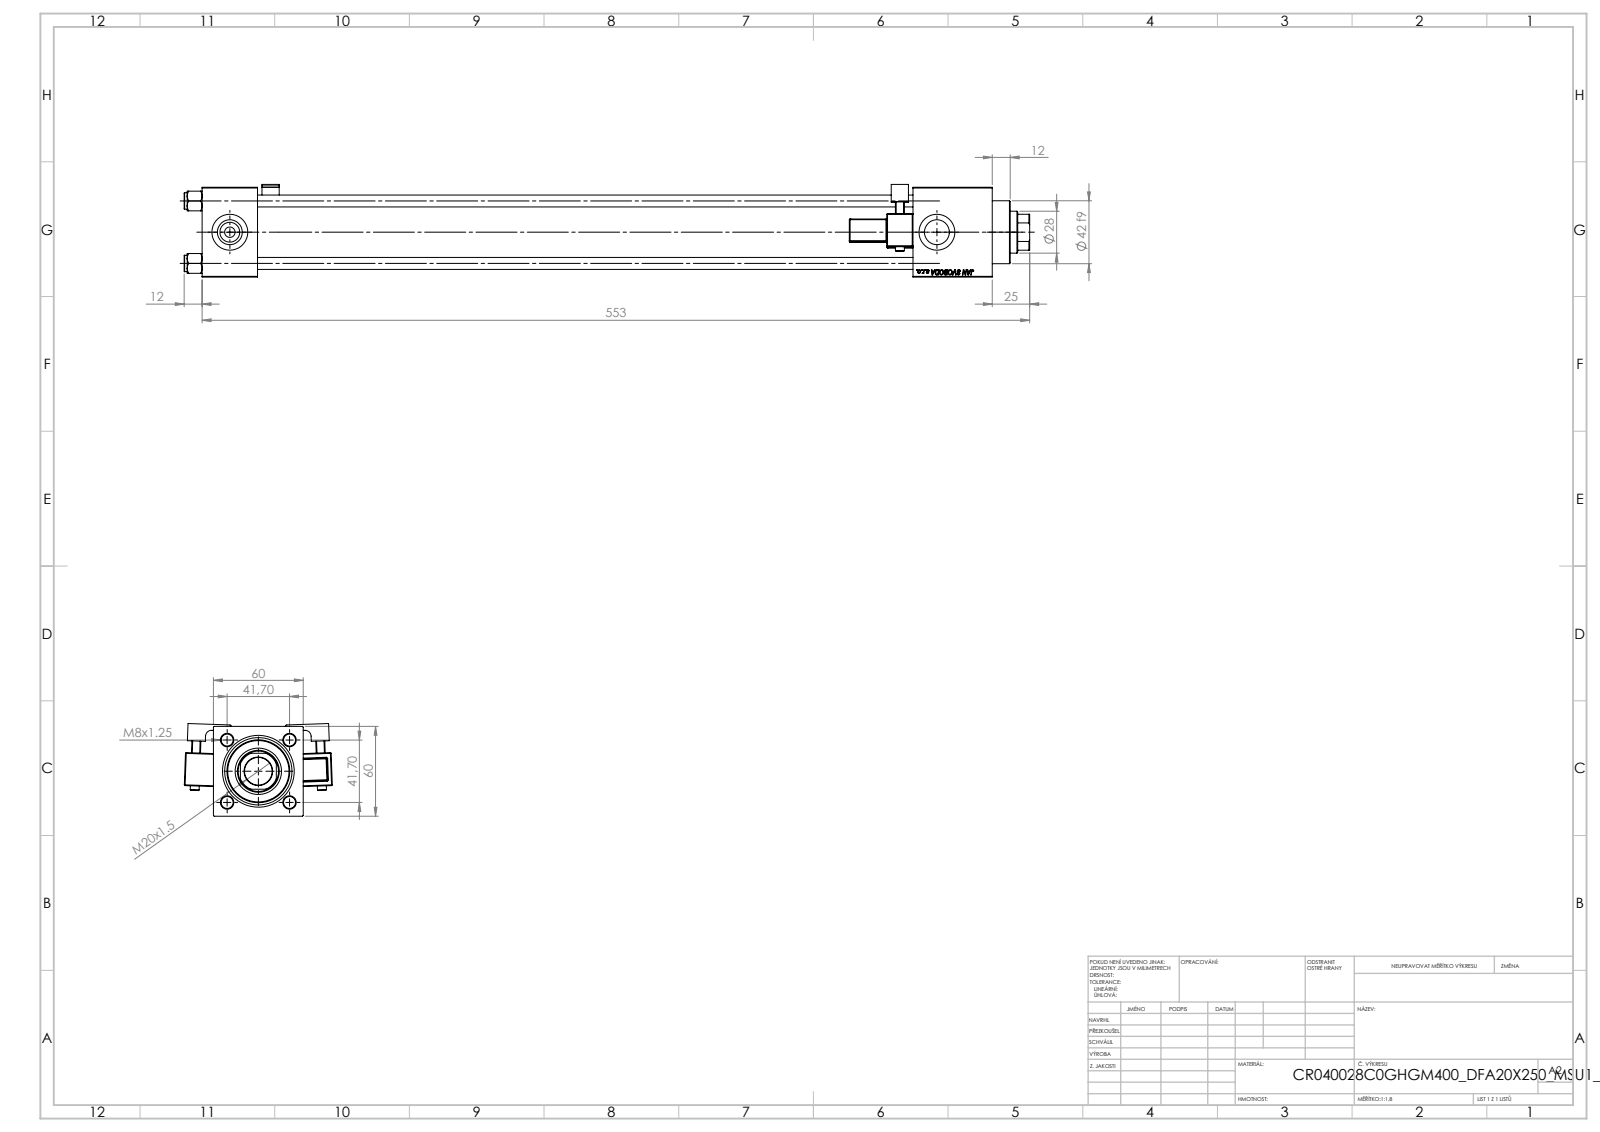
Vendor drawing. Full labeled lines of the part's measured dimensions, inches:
Part name (STEP PRODUCT): V215CR_VCP_C; NUT_M5_C; V215CR_MSU; V215CR_C_TYCINKA (+3 more)
STEP written by: SolidWorks 2019 (CONFIG_CONTROL_DESIGN)
Units: inches
Bodies: 14 solids, 1335 faces (596 planar, 155 cylindrical, 584 other)
Overall size (bounding box): 22.244 × 3.892 × 2.437
Volume: 58.2 in³ · Surface area: 473.5 in²
Round holes (diameter × count): ⌀0.315 ×4, ⌀0.276 ×2, ⌀0.656 ×2, ⌀0.945 ×2, ⌀0.728 ×1, ⌀1.102 ×1, ⌀1.22 ×1, ⌀1.575 ×1, ⌀1.772 ×1
Round bosses / shafts (diameter × count): ⌀0.433 ×4, ⌀0.236 ×2, ⌀1.811 ×1, ⌀1.654 ×1, ⌀1.417 ×1, ⌀1.181 ×1, ⌀0.787 ×1, ⌀0.709 ×1
Partial cylindrical surfaces — rounded edges, fillets, slot ends (radius × count): R0.02 ×48, R0.039 ×2, R0.098 ×2, R0.157 ×2, R0.295 ×1, R0.472 ×1, R0.531 ×1
Main face-to-face distances: 2.362, 1.457, 18.701, 17.244, 19.657, 18.201, 0.957, 2.087, 20.787, 19.331
Hole centre spacings: 1.161, 1.642, 2.322, 18.602
